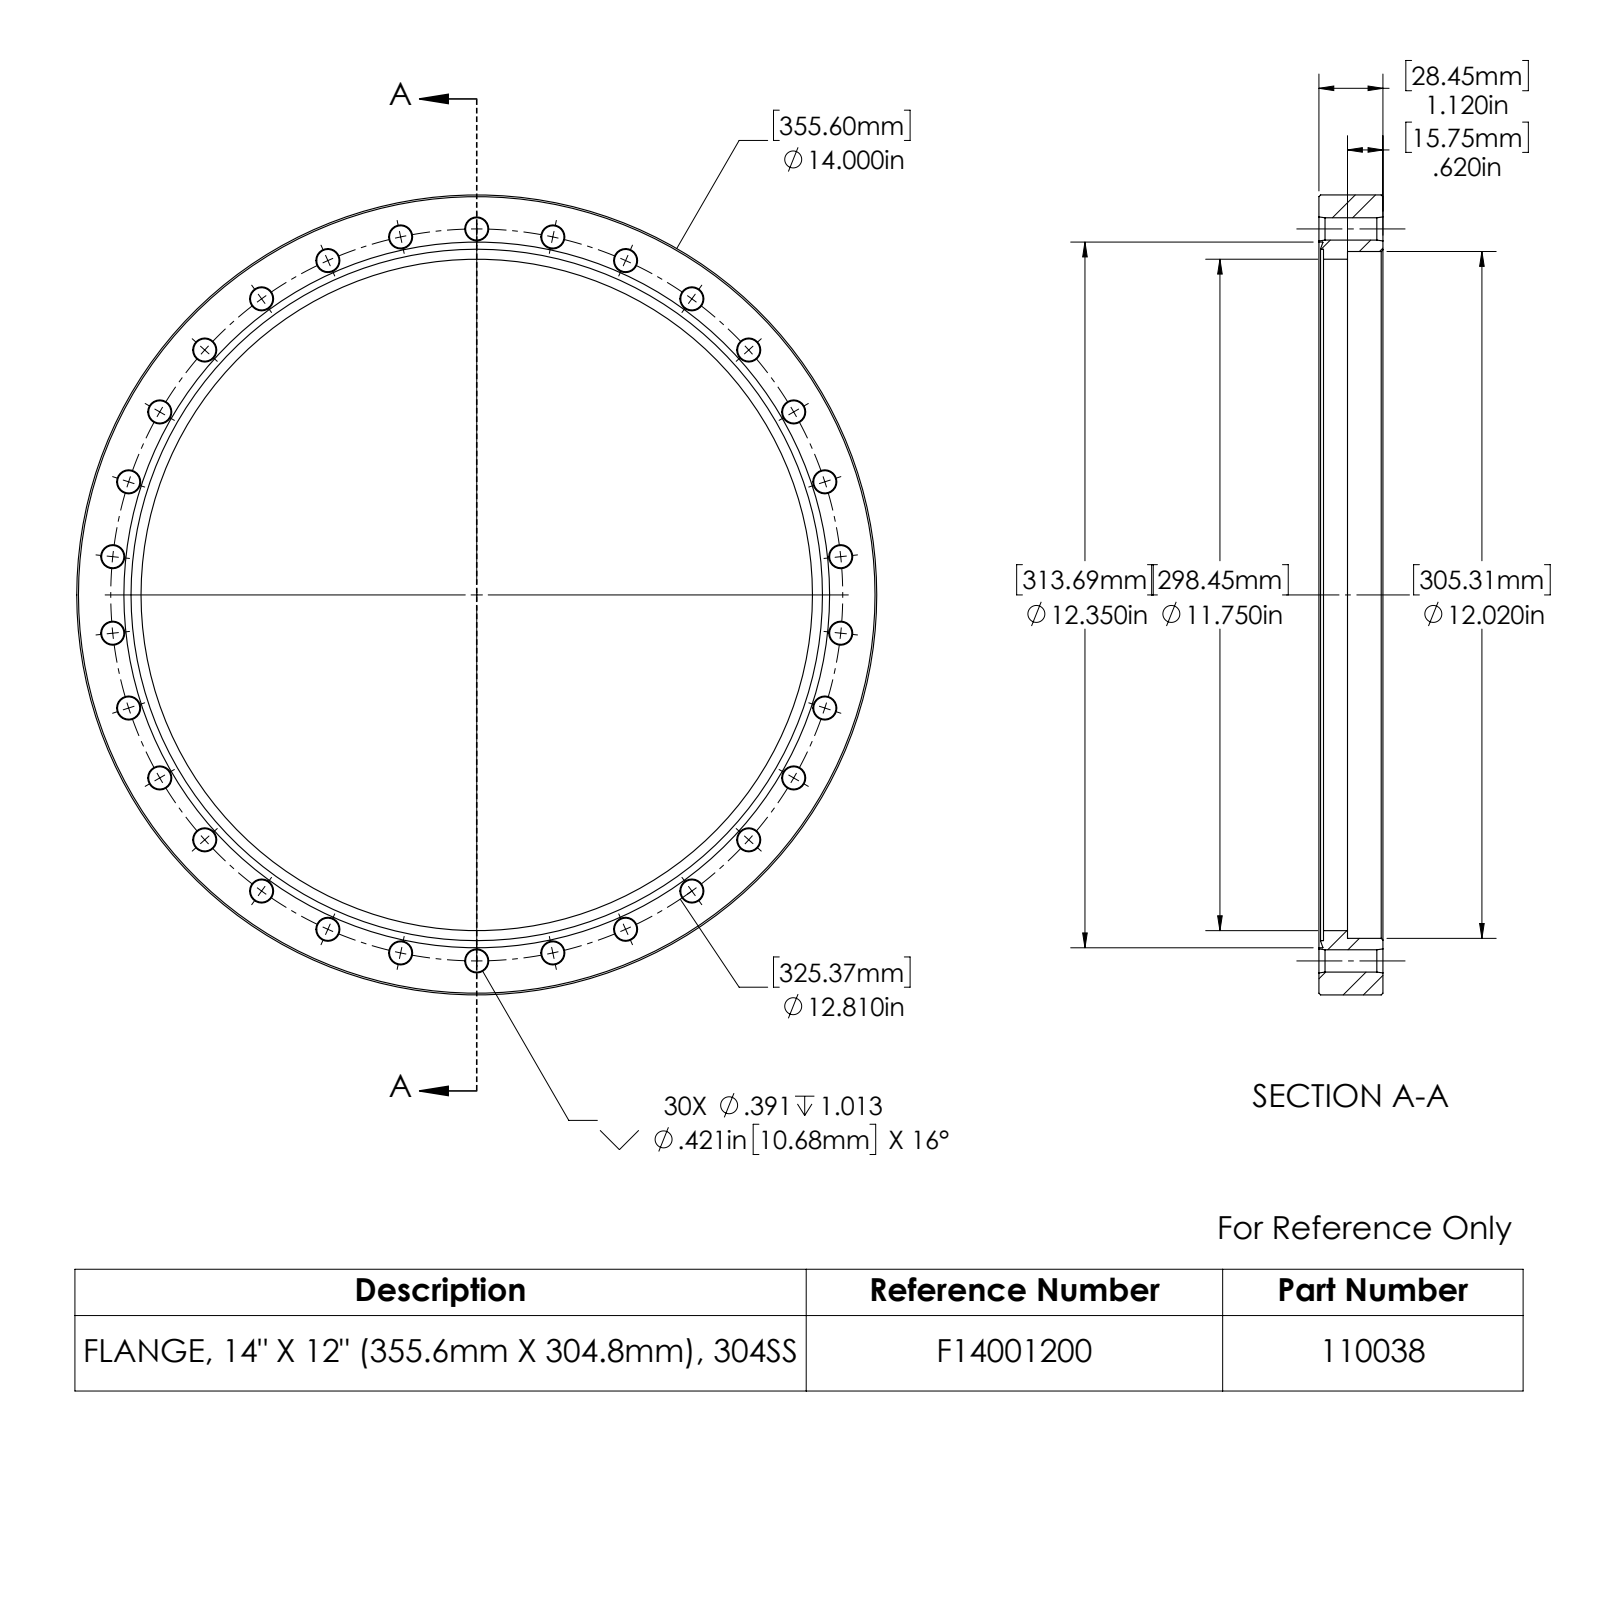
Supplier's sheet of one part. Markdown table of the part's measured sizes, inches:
| quantity | value |
| --- | --- |
| part name | 110038 |
| STEP written by | SolidWorks 2022 (AUTOMOTIVE_DESIGN) |
| units | inches |
| bodies | 1 solid, 210 faces (4 planar, 70 cylindrical, 136 other) |
| overall size | 14 × 14 × 1.12 |
| volume | 42.94 in³ |
| surface area | 214.9 in² |
| round holes (diameter × count) | 0.391 × 30, 11.75 × 1, 12.02 × 1, 12.1 × 1, 12.35 × 1 |
| round bosses / shafts (diameter × count) | 14 × 1 |
| main face-to-face distances | 1.12, 0.08, 1.04, 0.5, 0.42, 0.62 |
| hole center spacings | 1.339, 7.53, 10.363, 2.663, 3.959, 12.74, 5.21, 8.572 |
